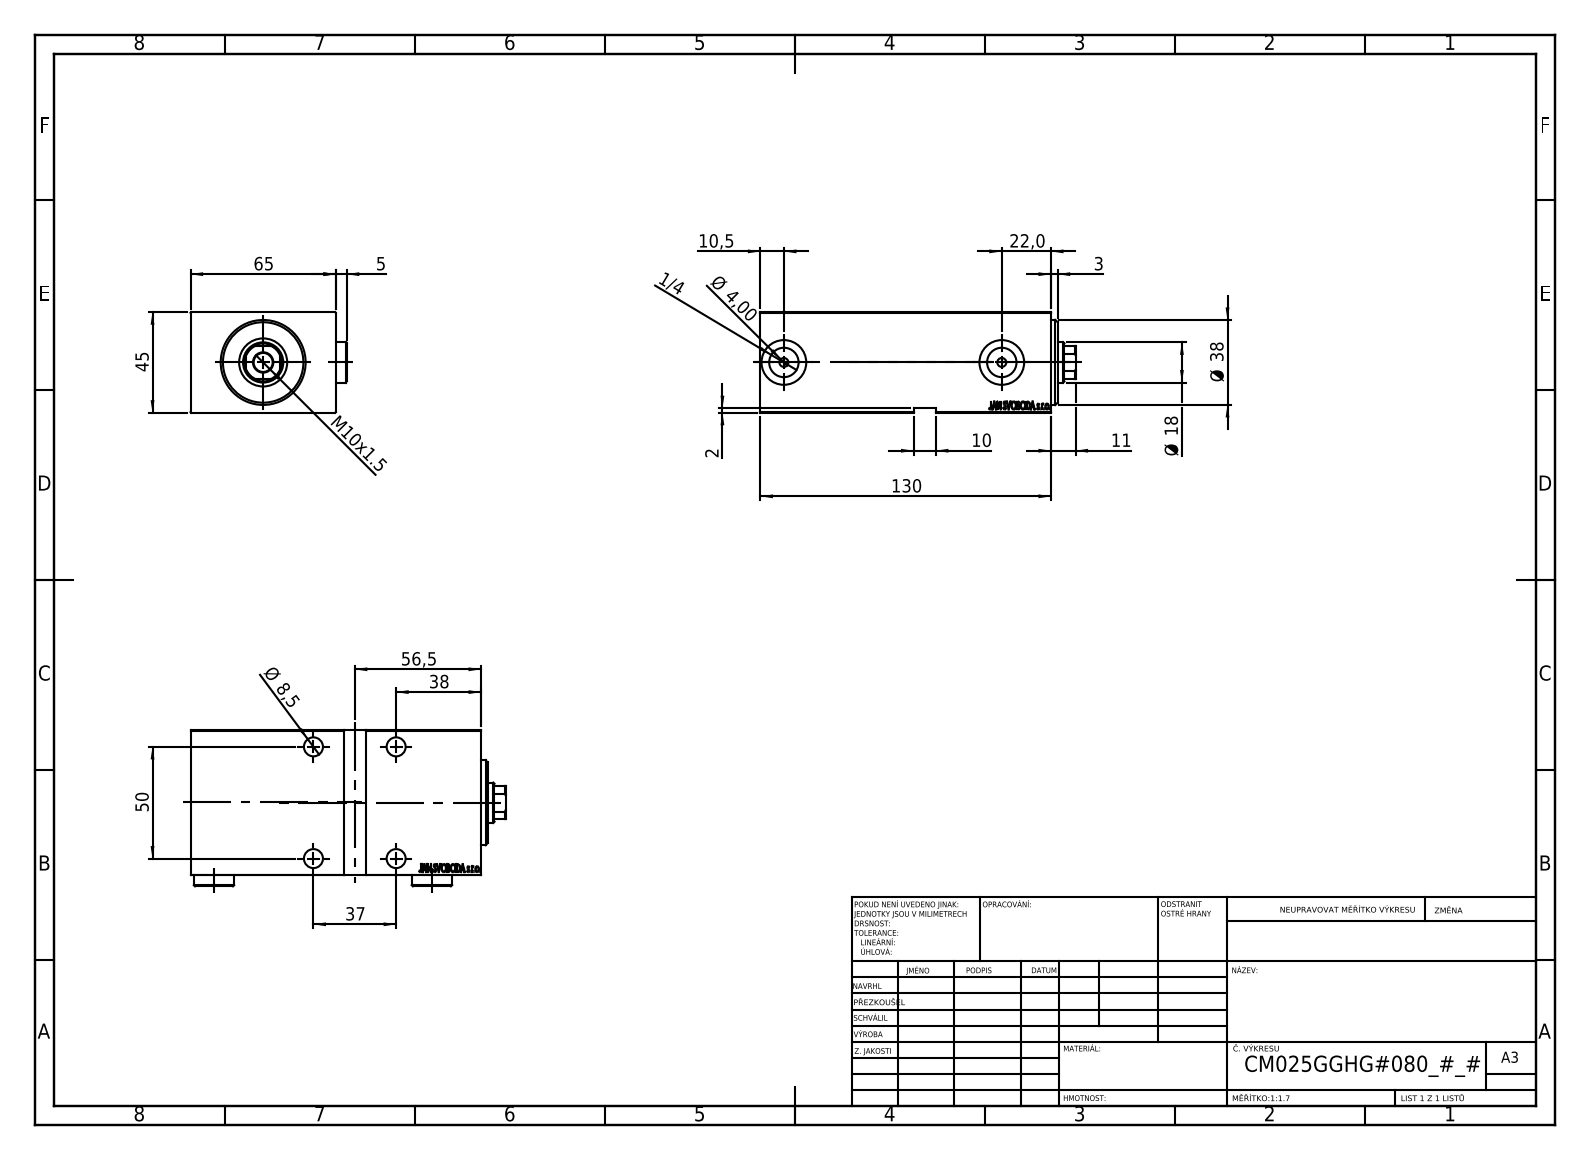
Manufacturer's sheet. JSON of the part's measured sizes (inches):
{"part_name": "V450CM_G_VCP; V450CM_G_Body; Zatka_OIL_PORT; V450CM_VC_G", "step_written_by": "SolidWorks 2019 (CONFIG_CONTROL_DESIGN)", "units": "inches", "bodies": {"solids": 5, "faces": 897, "planar": 441, "cylindrical": 58, "other": 398}, "overall_size": [5.551, 2.752, 1.772], "volume_in3": 21.25, "surface_area_in2": 102.6, "round_holes": [[0.335, 5], [0.531, 4], [0.157, 2], [0.518, 2], [0.787, 2], [0.709, 1], [0.846, 1], [0.984, 1], [1.063, 1], [1.378, 1]], "round_bosses_or_shafts": [[0.709, 2], [1.496, 1]], "partial_cylinders_radius": [[0.335, 1]], "face_to_face_distances": [1.772, 2.559, 5.118, 0.236, 4.685, 0.197, 4.882, 2.555, 0.315, 4.921], "hole_center_spacings": [1.457, 1.969, 2.449, 3.839]}
